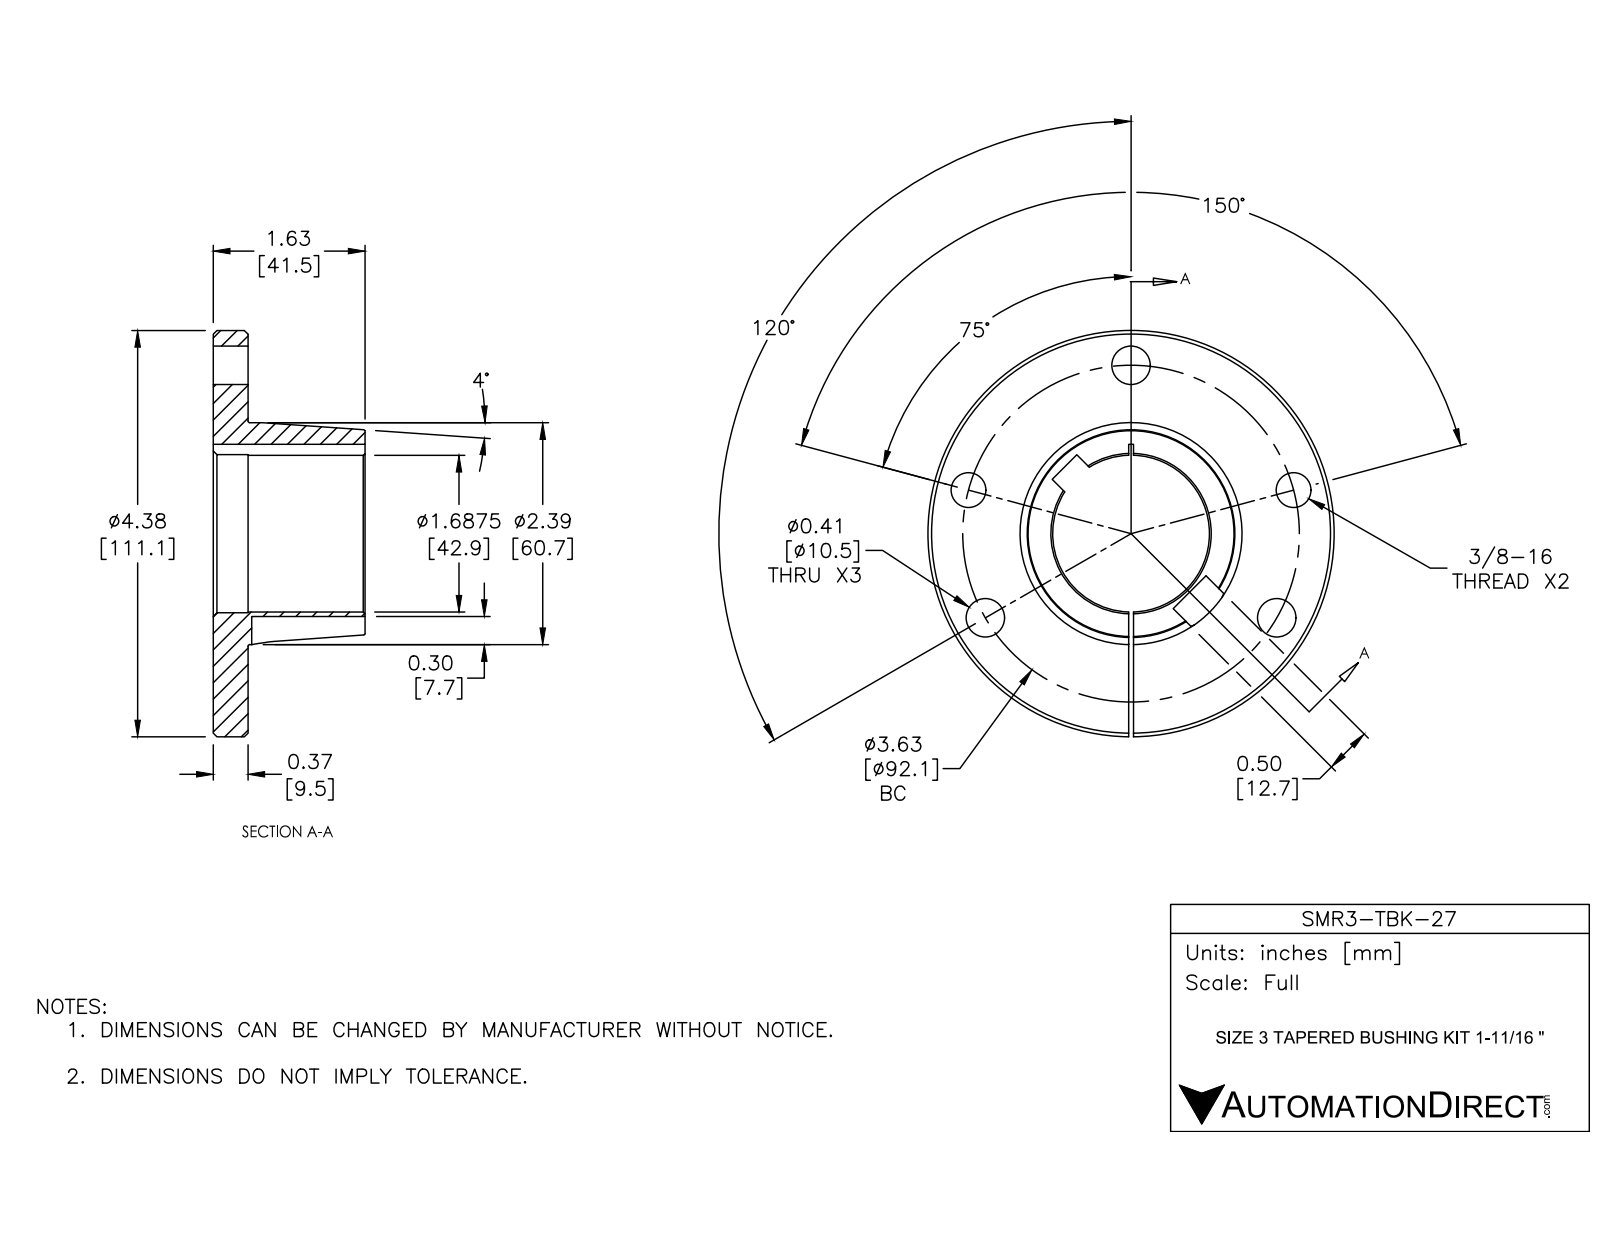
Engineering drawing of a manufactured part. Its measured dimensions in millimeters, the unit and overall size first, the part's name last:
Units: millimetres
Overall size (bounding box): 111.1 × 111.1 × 41.5
Round holes (diameter × count): ⌀10.5 ×3, ⌀8 ×2, ⌀9.5 ×2, ⌀42.9 ×1, ⌀43.3 ×1
Round bosses / shafts (diameter × count): ⌀111.1 ×1, ⌀60.7 ×1
Partial cylindrical surfaces — rounded edges, fillets, slot ends (radius × count): R6.4 ×1
Main face-to-face distances: 9.5, 41.5, 32, 1.3, 48.4, 1.6, 11.1, 9.5, 12.7
Hole centre spacings: 46.1, 79.7, 35.2, 56.1, 91.3, 89
Volume: 110 400 mm³ · Surface area: 33 300 mm²
Bodies: 1 solid, 108 faces (17 planar, 69 cylindrical, 22 other)
Part name (STEP PRODUCT): SMR3-TBK-27
STEP written by: SolidWorks 2016 (AUTOMOTIVE_DESIGN)
